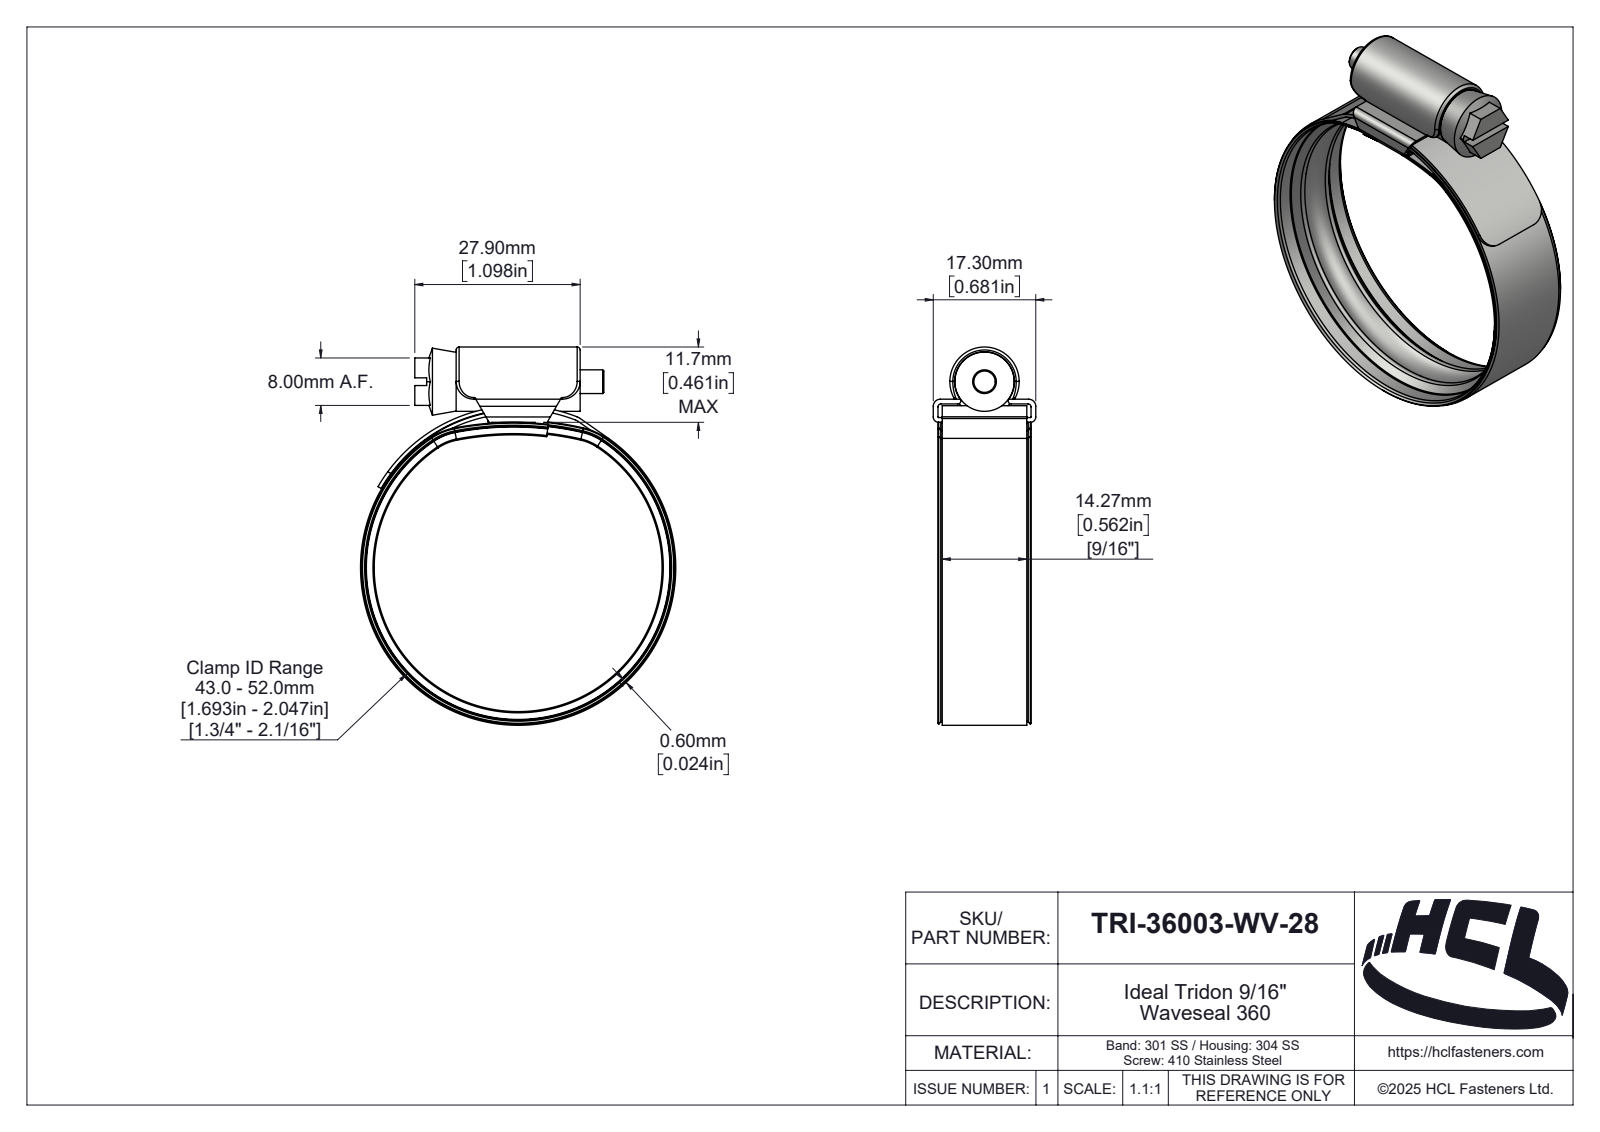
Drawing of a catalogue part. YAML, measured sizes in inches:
part_name: "TRI-36003-WV-28"
step_written_by: "SolidWorks 2025 (AUTOMOTIVE_DESIGN)"
units: inches
bodies: {solids: 4, faces: 418, planar: 42, cylindrical: 119, other: 257}
overall_size: [2.512, 2.094, 0.681]
volume: 0.312
surface_area: 22.66
round_holes:
  - {diameter: 2.024, count: 1}
  - {diameter: 2.047, count: 1}
round_bosses_or_shafts:
  - {diameter: 2.094, count: 1}
  - {diameter: 2.039, count: 1}
  - {diameter: 0.394, count: 1}
  - {diameter: 0.157, count: 1}
partial_cylinders:
  - {radius: 0.02, count: 6}
  - {radius: 0.118, count: 4}
  - {radius: 0.004, count: 2}
  - {radius: 0.035, count: 2}
  - {radius: 0.047, count: 2}
  - {radius: 0.39, count: 2}
  - {radius: 0.398, count: 2}
  - {radius: 0.018, count: 1}
face_to_face_distances: [0.031, 0.122, 0.561, 0.091, 0.024, 0.154, 1.098, 0.06, 0.621, 0.65]
